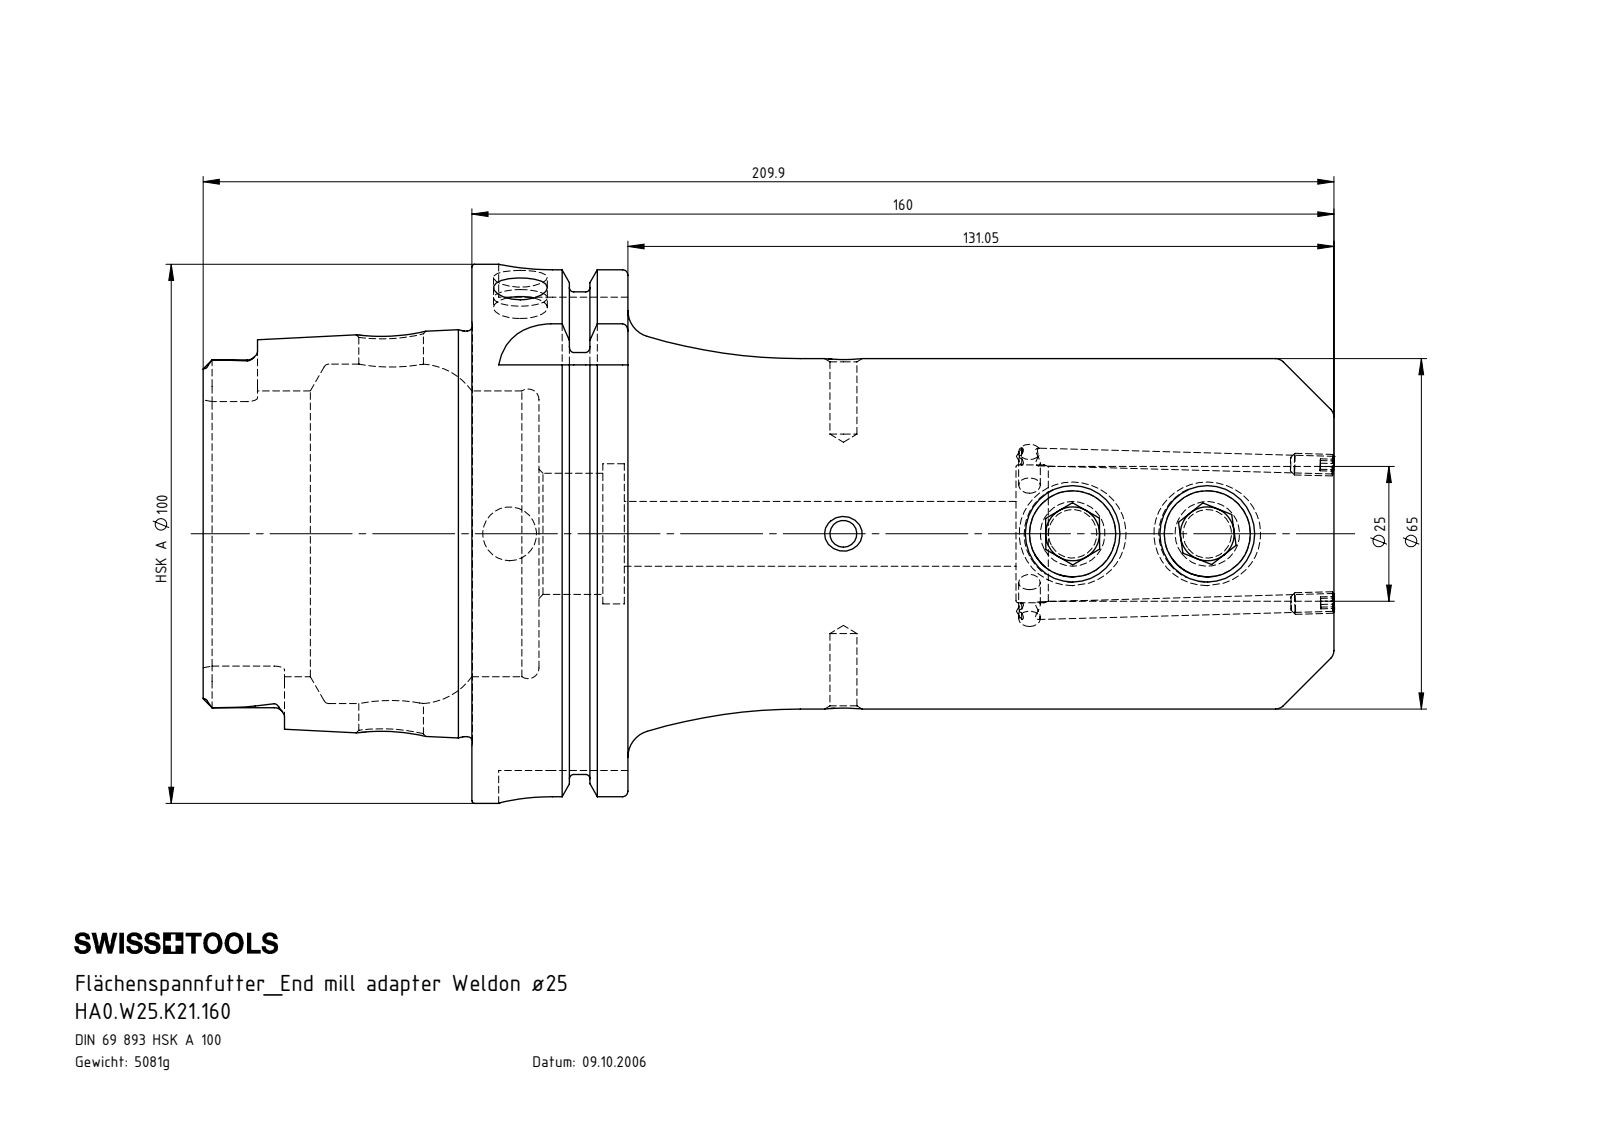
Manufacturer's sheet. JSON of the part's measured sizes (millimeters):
{"part_name": "ERU-CJ3.001.008_Default; HA0.W25.K21.160; HA0-W25.K21.160_D_Fertigbearbeitung; W25-ER1.001.020_Default", "step_written_by": "SolidWorks 2009 (CONFIG_CONTROL_DESIGN)", "units": "millimeters", "bodies": {"solids": 5, "faces": 311, "planar": 90, "cylindrical": 87, "other": 134}, "overall_size": [210, 100, 100], "volume_mm3": 647193, "surface_area_mm2": 89430, "round_holes": [[10, 3], [3.3, 2], [5, 2], [12, 2], [16, 2], [4, 1], [22.5, 1], [25, 1], [25.6, 1], [26, 1], [53, 1], [63, 1]], "round_bosses_or_shafts": [[18, 2], [4, 2], [100, 1], [91.95, 1], [75.26, 1], [65, 1]], "partial_cylinders_radius": [[1.9, 6], [4.88, 4], [10, 4]], "face_to_face_distances": [28.95, 12.45, 16.5, 160, 147.55, 131.05, 49.9, 62.35, 78.85, 209.9], "hole_center_spacings": [25, 42.55, 61.95, 67.55, 83.95, 104.5, 129.5]}
